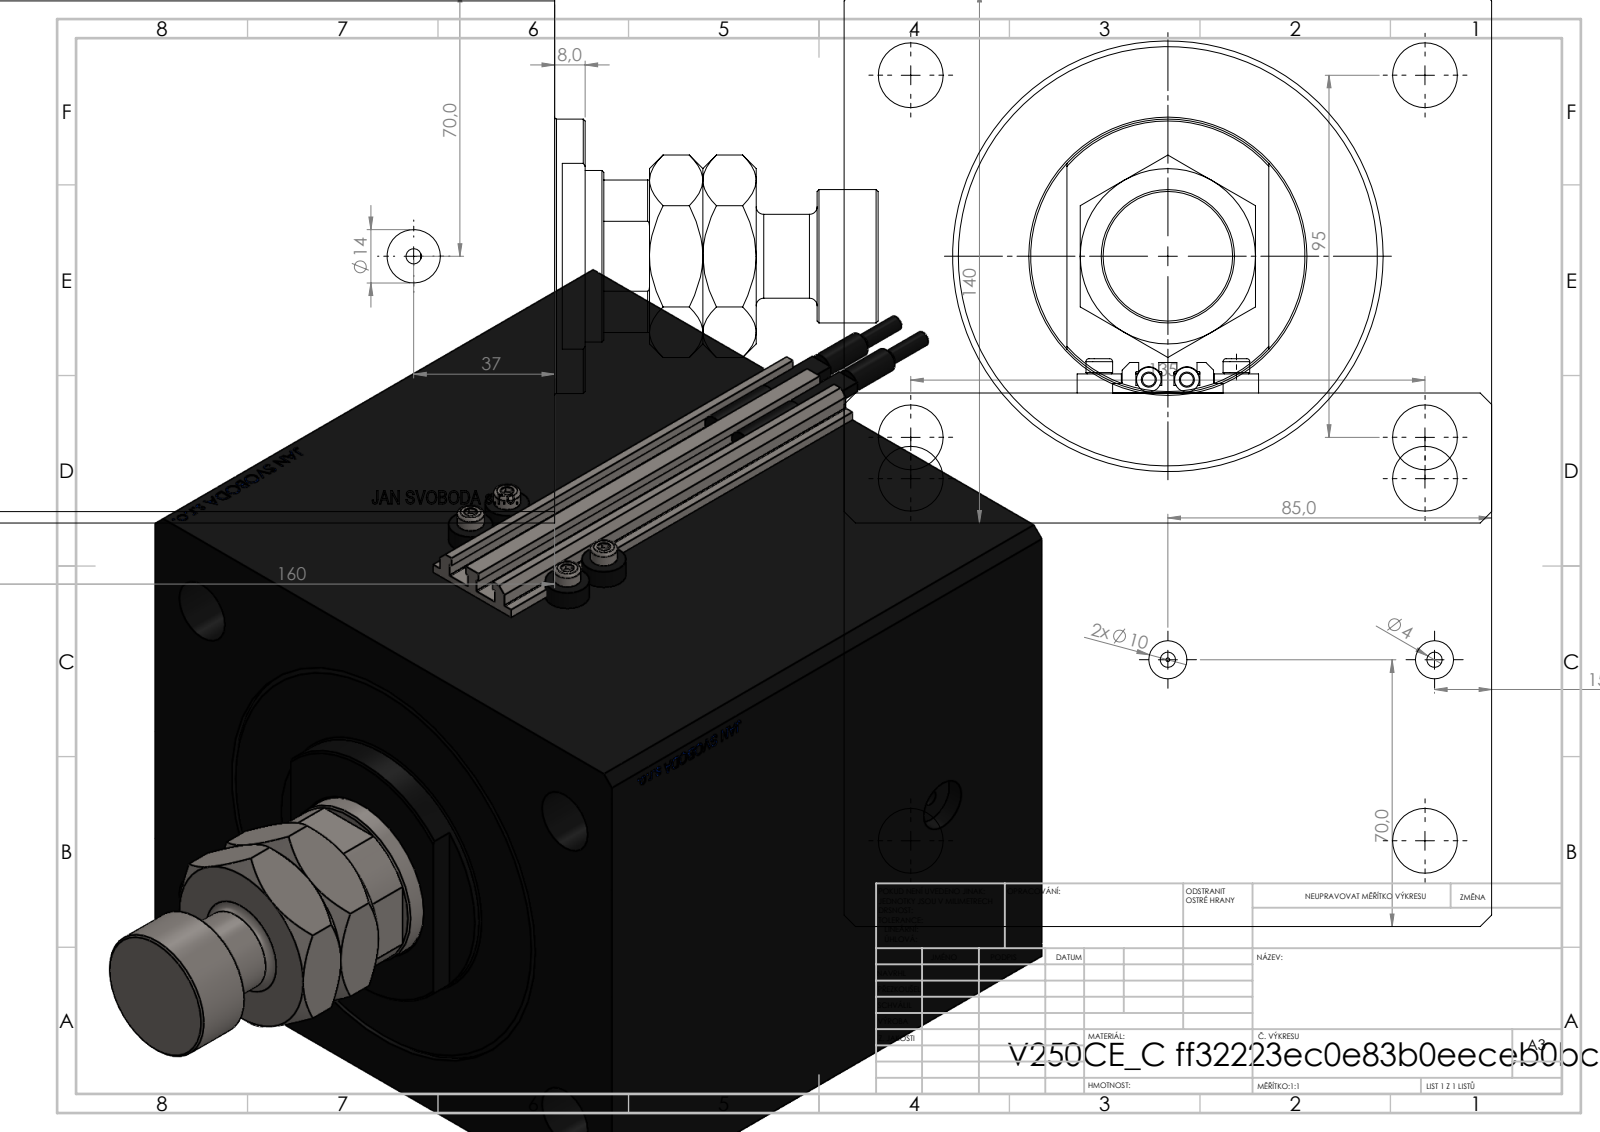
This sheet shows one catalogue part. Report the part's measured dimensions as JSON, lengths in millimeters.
{"part_name": "V250CE_C_VCP; MFA; SWITCH_V250CE; V250CE_C_Body (+2 more)", "step_written_by": "SolidWorks 2019 (CONFIG_CONTROL_DESIGN)", "units": "millimeters", "bodies": {"solids": 11, "faces": 1142, "planar": 552, "cylindrical": 104, "other": 486}, "overall_size": [280.9, 170, 149], "volume_mm3": 3445000, "surface_area_mm2": 341358, "round_holes": [[4, 8], [17, 4], [10, 2], [14, 2], [1.25, 1], [31.5, 1], [45, 1], [100, 1], [113, 1]], "round_bosses_or_shafts": [[11.6, 4], [7, 4], [6.8, 2], [6.5, 2], [4, 2], [72, 1], [35, 1], [22, 1]], "partial_cylinders_radius": [[0.2, 10], [22, 1]], "face_to_face_distances": [140, 170, 160, 28.9, 131.1, 124.9, 96, 35.1, 46, 50], "hole_center_spacings": [82.54, 13.6, 36, 38.48, 47.57, 95, 135, 145.47]}
